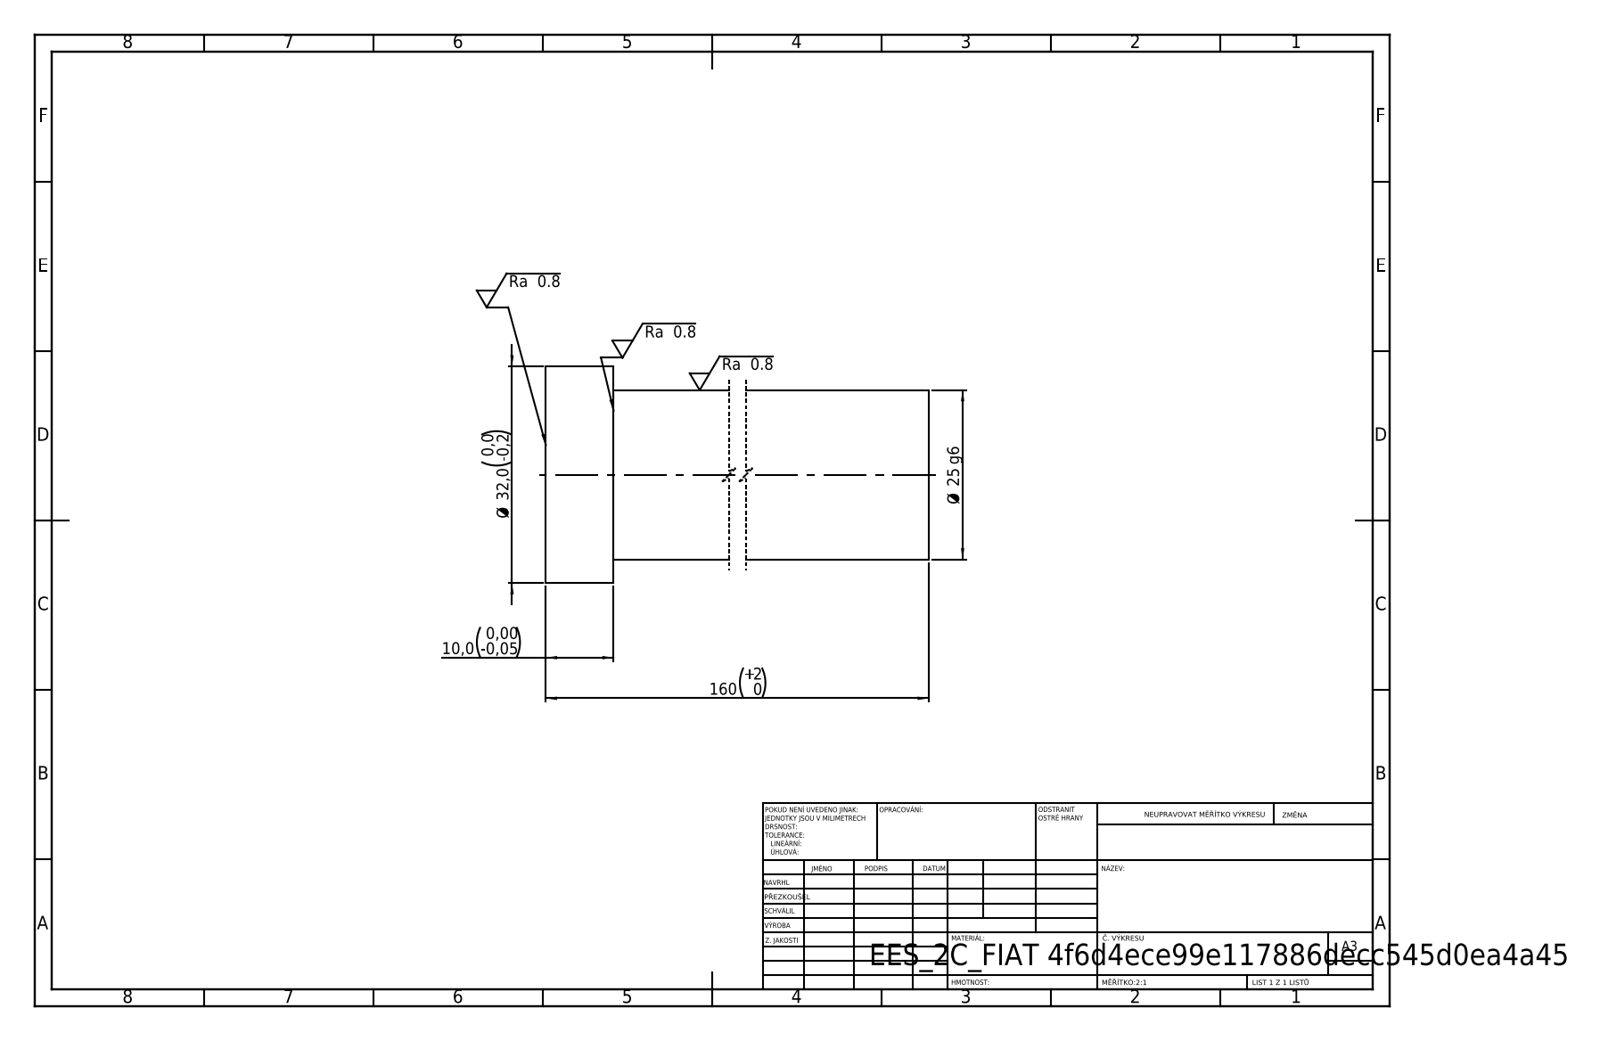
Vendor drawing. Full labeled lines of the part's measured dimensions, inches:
STEP written by: SolidWorks 2019 (CONFIG_CONTROL_DESIGN)
Units: inches
Bodies: 1 solid, 7 faces (3 planar, 4 cylindrical, 0 other)
Overall size (bounding box): 6.299 × 1.26 × 1.26
Volume: 4.984 in³ · Surface area: 22.31 in²
Round bosses / shafts (diameter × count): ⌀1.26 ×1, ⌀0.984 ×1
Main face-to-face distances: 6.299, 0.394, 5.906
